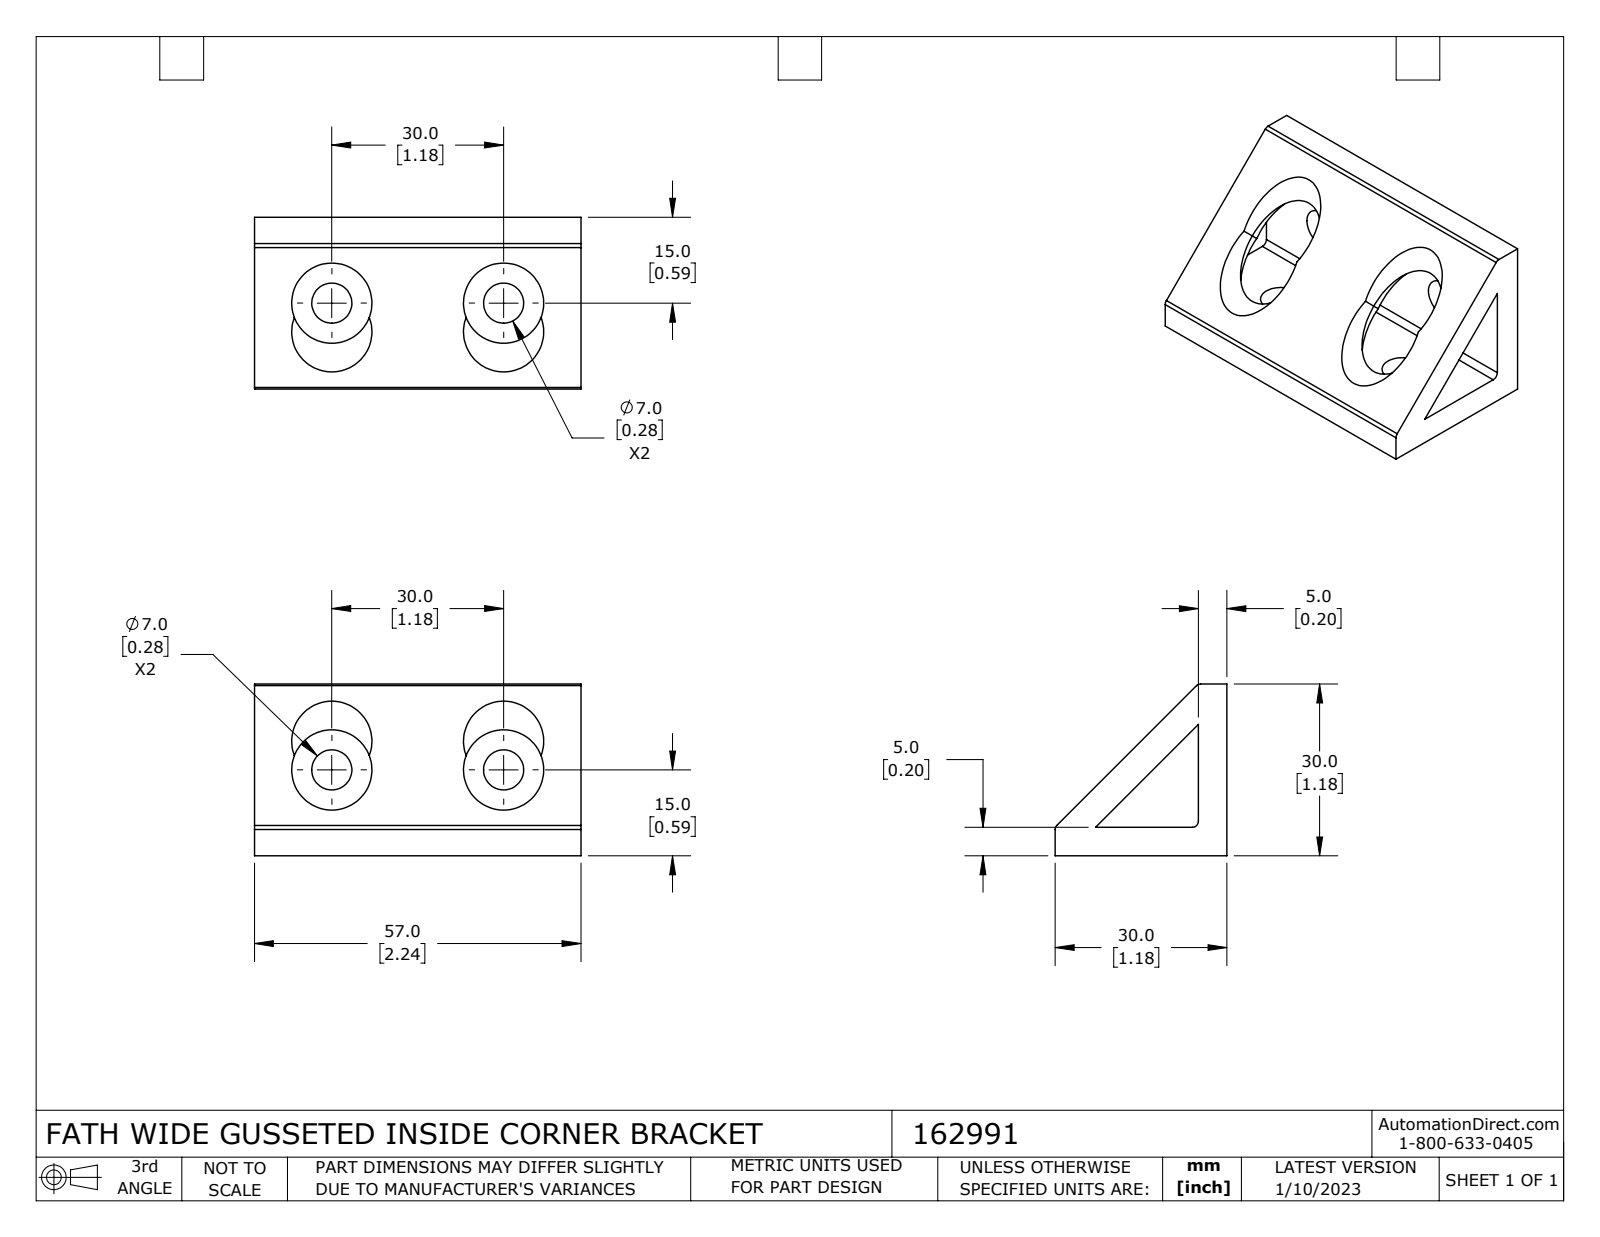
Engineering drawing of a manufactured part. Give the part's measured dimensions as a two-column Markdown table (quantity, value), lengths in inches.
| quantity | value |
| --- | --- |
| part name | 162991 |
| STEP written by | SolidWorks 2021 (CONFIG_CONTROL_DESIGN) |
| units | inches |
| bodies | 1 solid, 33 faces (10 planar, 23 cylindrical, 0 other) |
| overall size | 2.244 × 1.181 × 1.181 |
| volume | 1.28 in³ |
| surface area | 15.47 in² |
| round holes (diameter × count) | 0.276 × 4, 0.551 × 4 |
| partial cylindrical surfaces (radius × count) | 0.039 × 3 |
| main face-to-face distances | 0.197, 0.196, 0.984, 1.181, 2.244 |
| hole center spacings | 1.181 |
